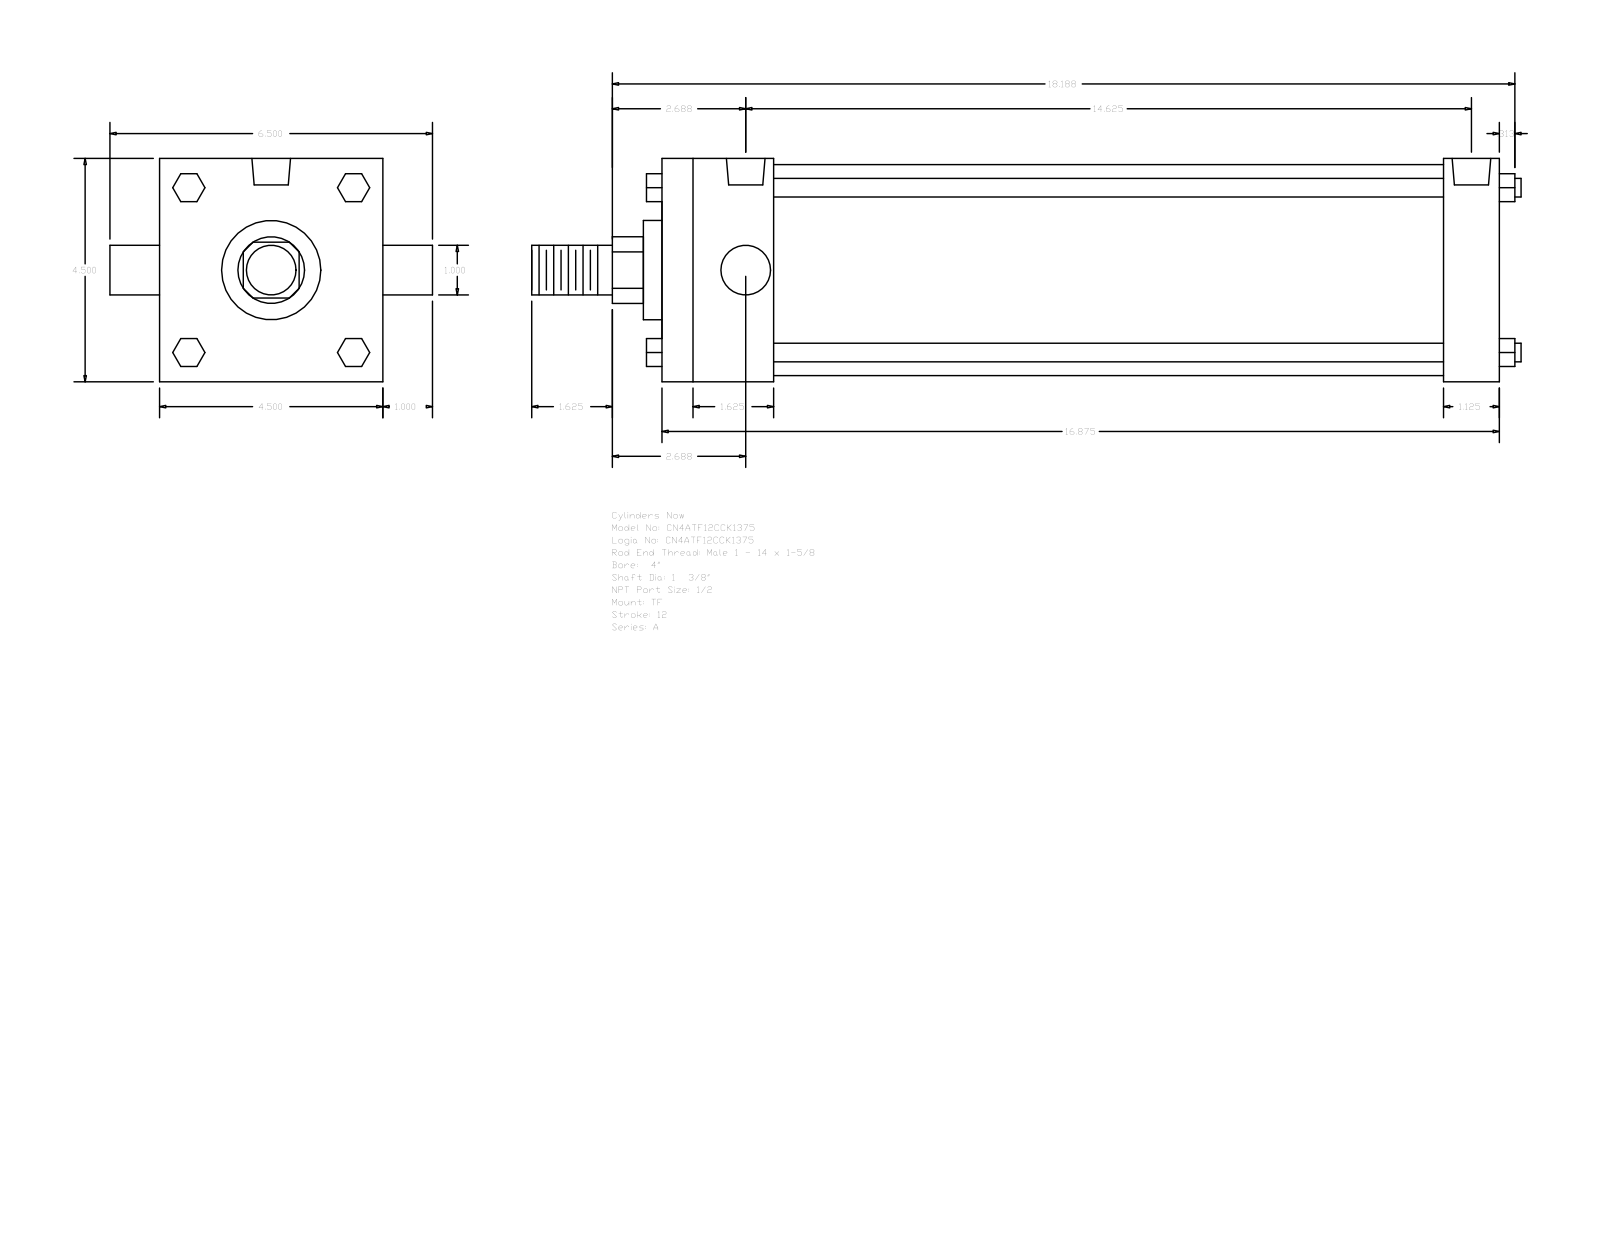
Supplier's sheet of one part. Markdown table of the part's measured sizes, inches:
| quantity | value |
| --- | --- |
| part name | A_TF__0400_1.375 |
| STEP written by | GSSL Pune (CONFIG_CONTROL_DESIGN) |
| units | inches |
| bodies | 0 solids, 120 faces (92 planar, 28 cylindrical, 0 other) |
| overall size | 19.937 × 6.5 × 4.5 |
| round holes (diameter × count) | 0.344 × 3, 0.778 × 2 |
| round bosses / shafts (diameter × count) | 0.375 × 4, 1 × 2, 4.25 × 1, 2 × 1, 1.375 × 1 |
| partial cylindrical surfaces (radius × count) | 0.672 × 1 |
| main face-to-face distances | 4.5, 16.875, 2.25, 15.75, 1.125, 13.5, 14.625, 2.625, 0.563, 1 |
| hole center spacings | 0.125, 14.5, 14.375, 14.625 |
